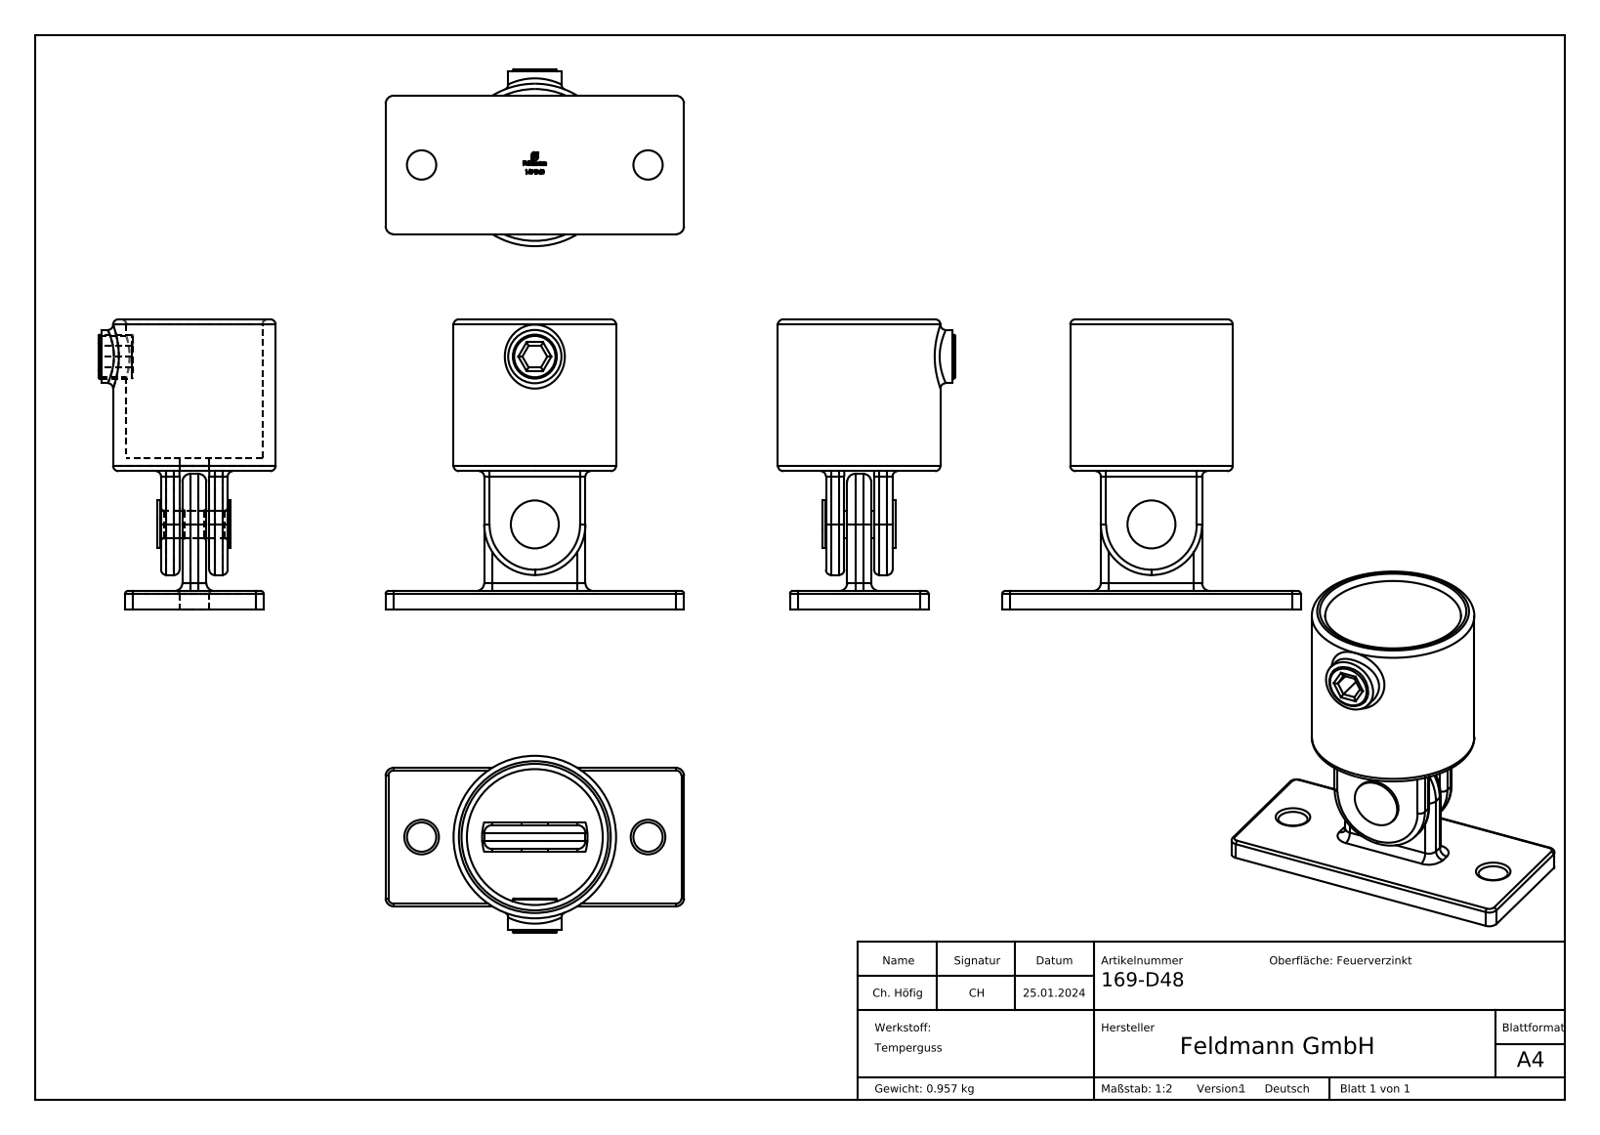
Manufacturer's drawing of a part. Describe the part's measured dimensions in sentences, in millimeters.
The part is named "169-D48 Teil3_169-D48 Teil3; 169-D48 Teil4_169-D48 Teil4; 169-D48; 169-D48 Teil1_169-D48 Teil1 (+1 more)". Its 3-D file was written by "SolidWorks 2018 (CONFIG_CONTROL_DESIGN)". It is 4 solids with 382 faces: 170 planar, 62 cylindrical and 150 other. Overall it measures 112 by 109 by 66.5 millimeters. Its volume is 130 784 cubic millimeters and its surface area 50 776 square millimeters. Round holes: 2 of diameter 11, 1 of diameter 10.5, 1 of diameter 15.25, 1 of diameter 51. Round bosses or shafts: 1 of diameter 61, 1 of diameter 38, 1 of diameter 20, 1 of diameter 18, 1 of diameter 16.5, 1 of diameter 10. Partial cylindrical surfaces (rounded edges, fillets, slot ends): 24 of radius 2, 12 of radius 3, 4 of radius 1, 1 of radius 19.81. The main face-to-face distances are 7, 52, 1.1, 10.1, 6.9, 8, 17, 18.1, 57, 50. The hole center spacings are 42.5, 63, 85.
